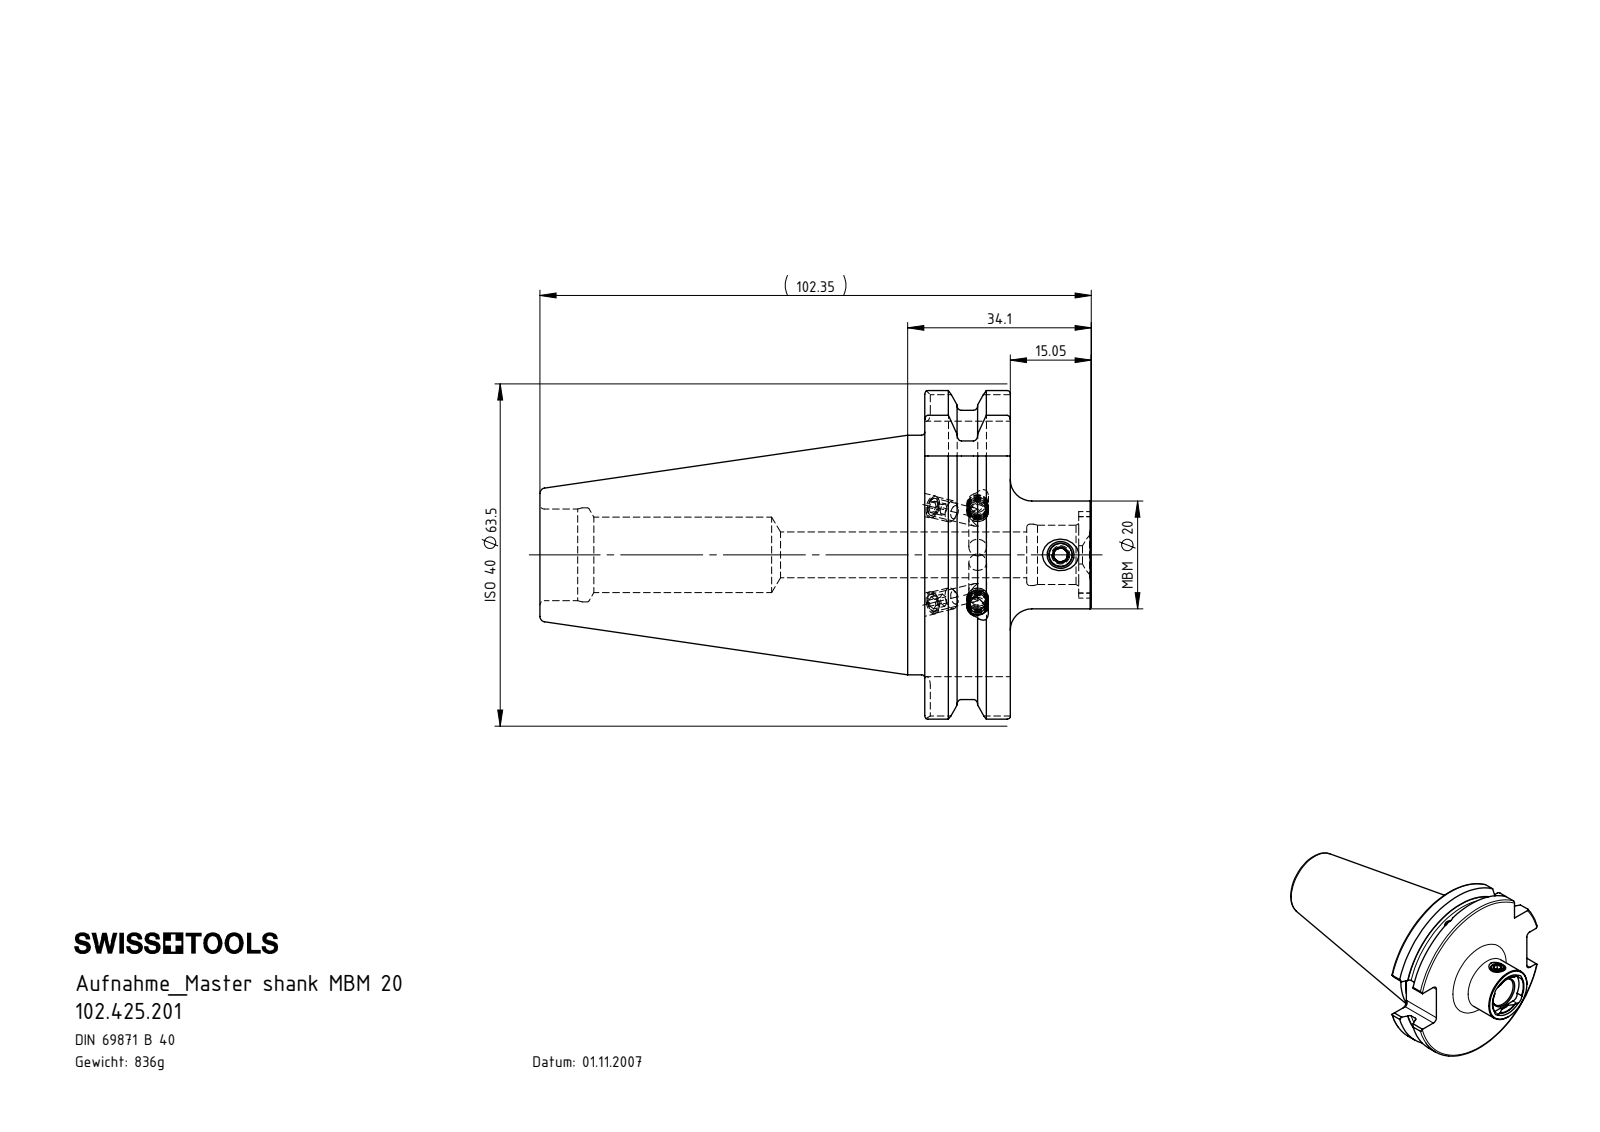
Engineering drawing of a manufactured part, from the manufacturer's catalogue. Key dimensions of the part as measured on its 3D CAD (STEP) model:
Part name (STEP PRODUCT): SB3-MB5.K01.039_C_mit Bundkhlung; 102.425.201; MB5-ER1.001.017_A
STEP written by: SolidWorks 2017 (CONFIG_CONTROL_DESIGN)
Units: millimetres
Bodies: 2 solids, 212 faces (49 planar, 65 cylindrical, 98 other)
Overall size (bounding box): 86.75 × 55 × 55
Volume: 67 180 mm³ · Surface area: 20 445 mm²
Round holes (diameter × count): ⌀4 ×2, ⌀4.2 ×1, ⌀6 ×1, ⌀8.5 ×1, ⌀10.2 ×1, ⌀11 ×1, ⌀13 ×1, ⌀13.45 ×1, ⌀30 ×1, ⌀30.6 ×1
Round bosses / shafts (diameter × count): ⌀55 ×1, ⌀31.75 ×1, ⌀12 ×1
Partial cylindrical surfaces — rounded edges, fillets, slot ends (radius × count): R1.6 ×8, R5.2 ×4, R8 ×1, R8.05 ×1, R18.5 ×1, R21.27 ×1, R22.02 ×1, R24.98 ×1
Main face-to-face distances: 4.9, 35.9, 31, 31.35, 26.45, 4.55, 35, 35.35, 30.45, 4
